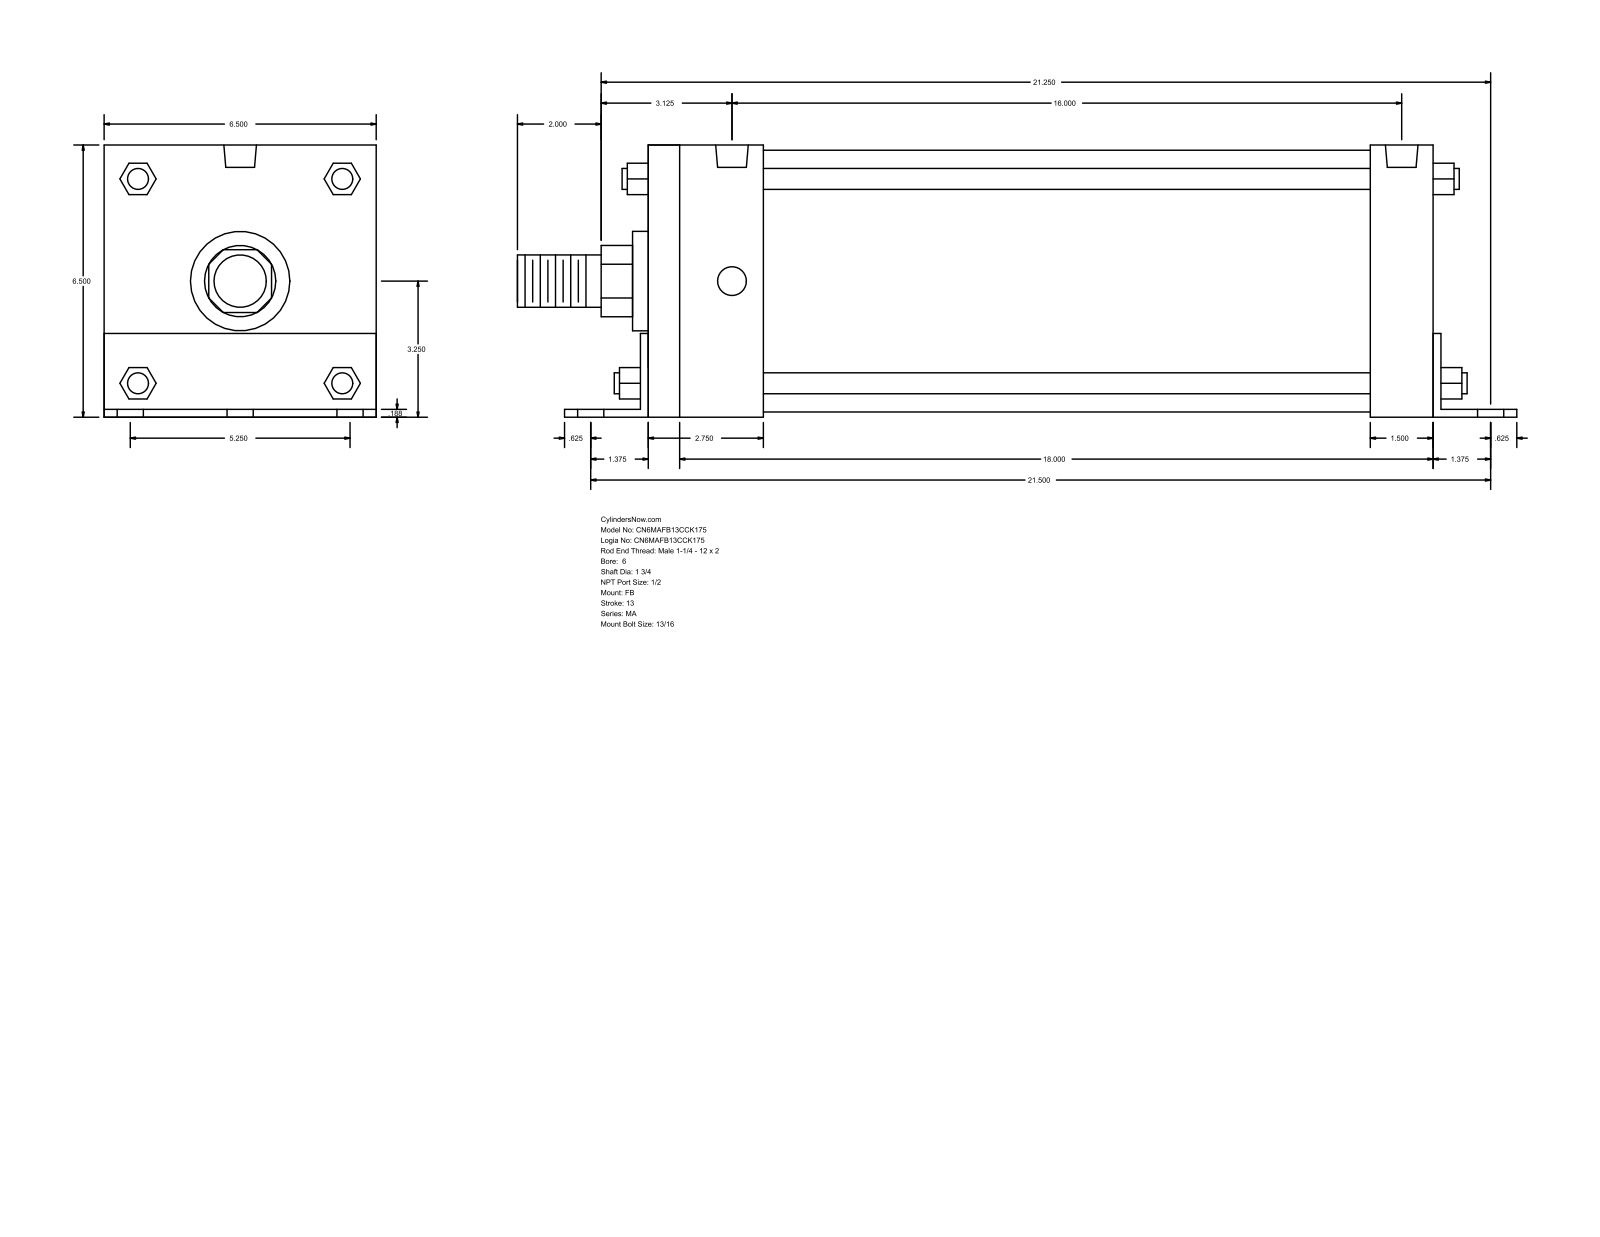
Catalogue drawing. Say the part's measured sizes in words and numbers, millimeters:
The part is named "MA_FB__0600_1.75". Its 3-D file was written by "GSSL Pune (CONFIG_CONTROL_DESIGN)". It is 0 solids with 140 faces: 105 planar, 35 cylindrical and 0 other. Overall it measures 606.42 by 165.15 by 165.1 millimeters. Round holes: 6 of diameter 20.64, 4 of diameter 17.46, 2 of diameter 19.77. Round bosses or shafts: 4 of diameter 12.7, 1 of diameter 158.75, 1 of diameter 60.33, 1 of diameter 44.45, 1 of diameter 31.75. Partial cylindrical surfaces (rounded edges, fillets, slot ends): 1 of radius 21.63, 1 of radius 32.05. The main face-to-face distances are 165.1, 4.76, 476.25, 165.15, 4.71, 160.39, 69.85, 74.61, 4.77, 481.02. The hole center spacings are 66.67, 550.15, 546.1, 85.78, 108.6, 133.34, 406.39, 465.17.
